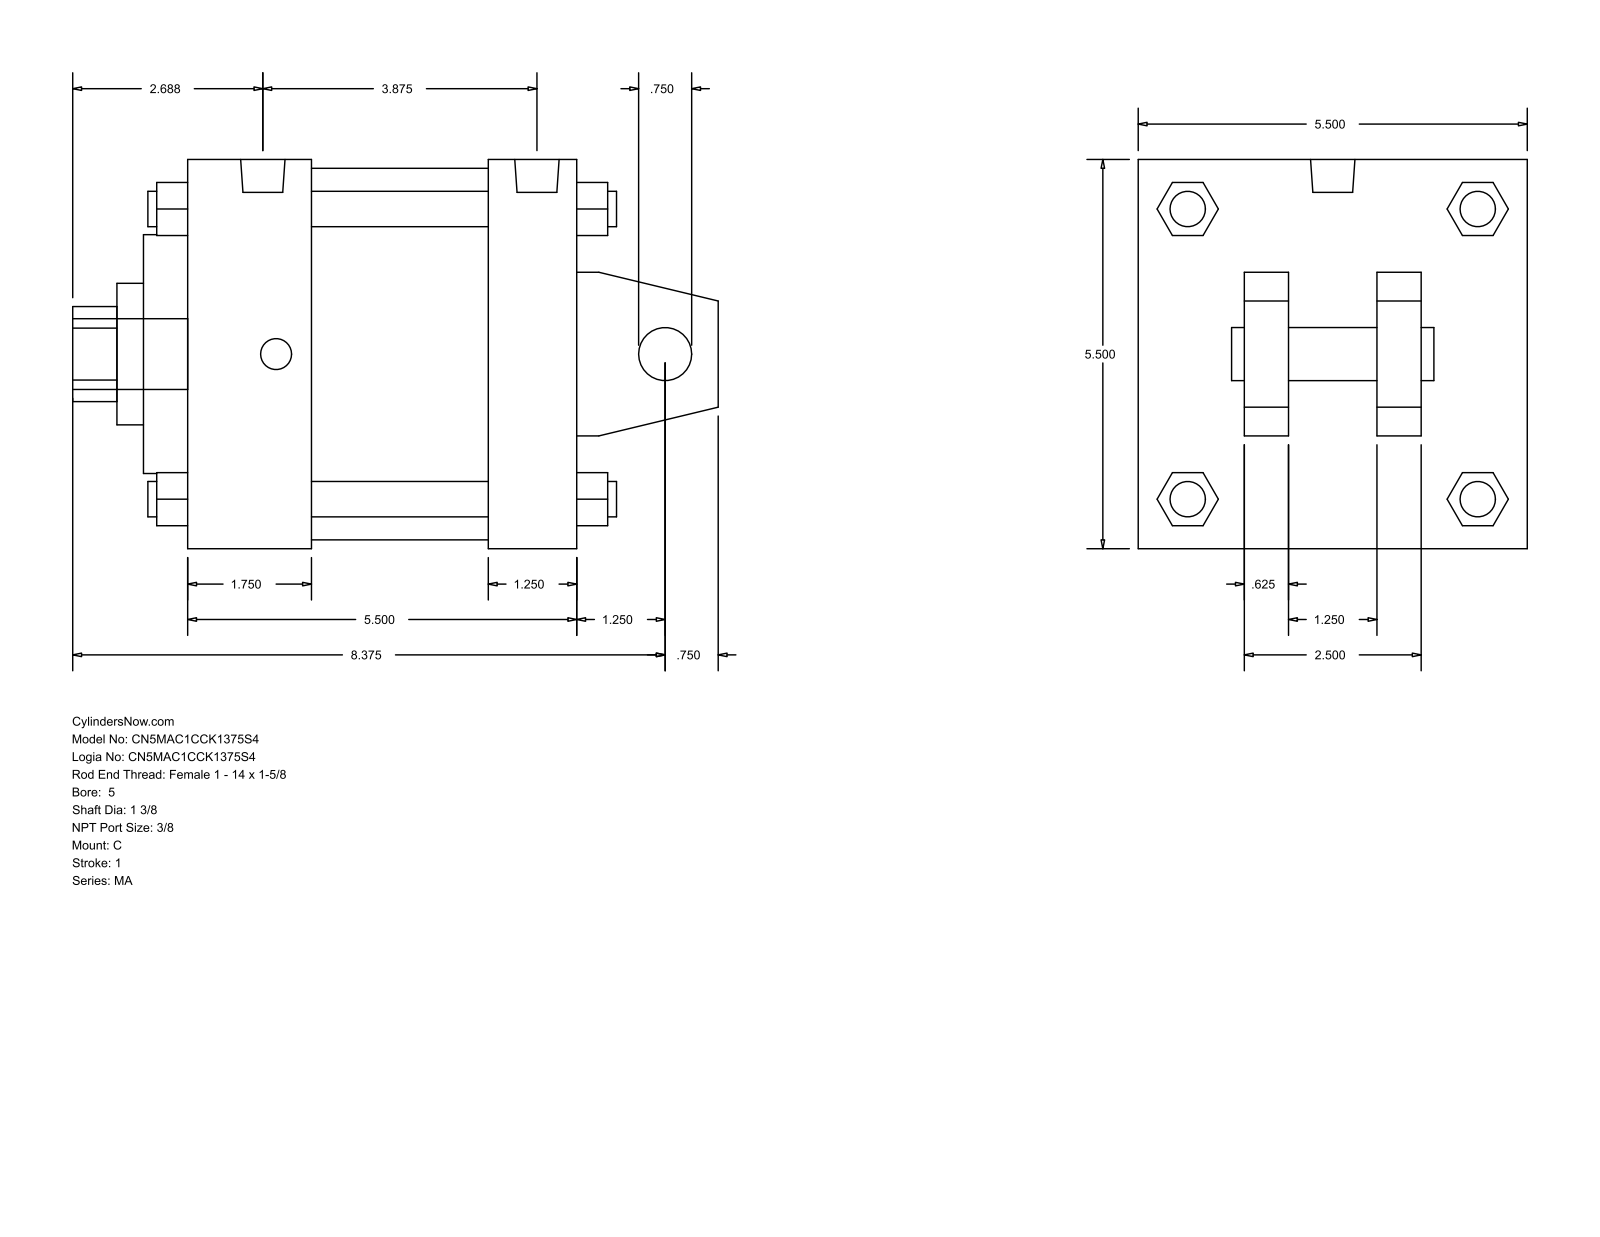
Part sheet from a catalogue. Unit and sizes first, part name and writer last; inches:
Units: inches
Overall size (bounding box): 9.125 × 5.5 × 5.5
Round holes (diameter × count): ⌀0.75 ×1, ⌀1.375 ×1, ⌀2 ×1, ⌀3.375 ×1, ⌀5.25 ×1
Round bosses / shafts (diameter × count): ⌀0.5 ×4, ⌀0.437 ×4, ⌀0.627 ×2, ⌀1 ×1
Partial cylindrical surfaces — rounded edges, fillets, slot ends (radius × count): R0.672 ×1
Main face-to-face distances: 5.5, 0.625, 2.5, 4.25, 1.25, 1.75, 3.75, 1.5, 4, 2.125
Bodies: 0 solids, 141 faces (109 planar, 32 cylindrical, 0 other)
Part name (STEP PRODUCT): MA_C__0500_1.375
STEP written by: GSSL Pune (CONFIG_CONTROL_DESIGN)
